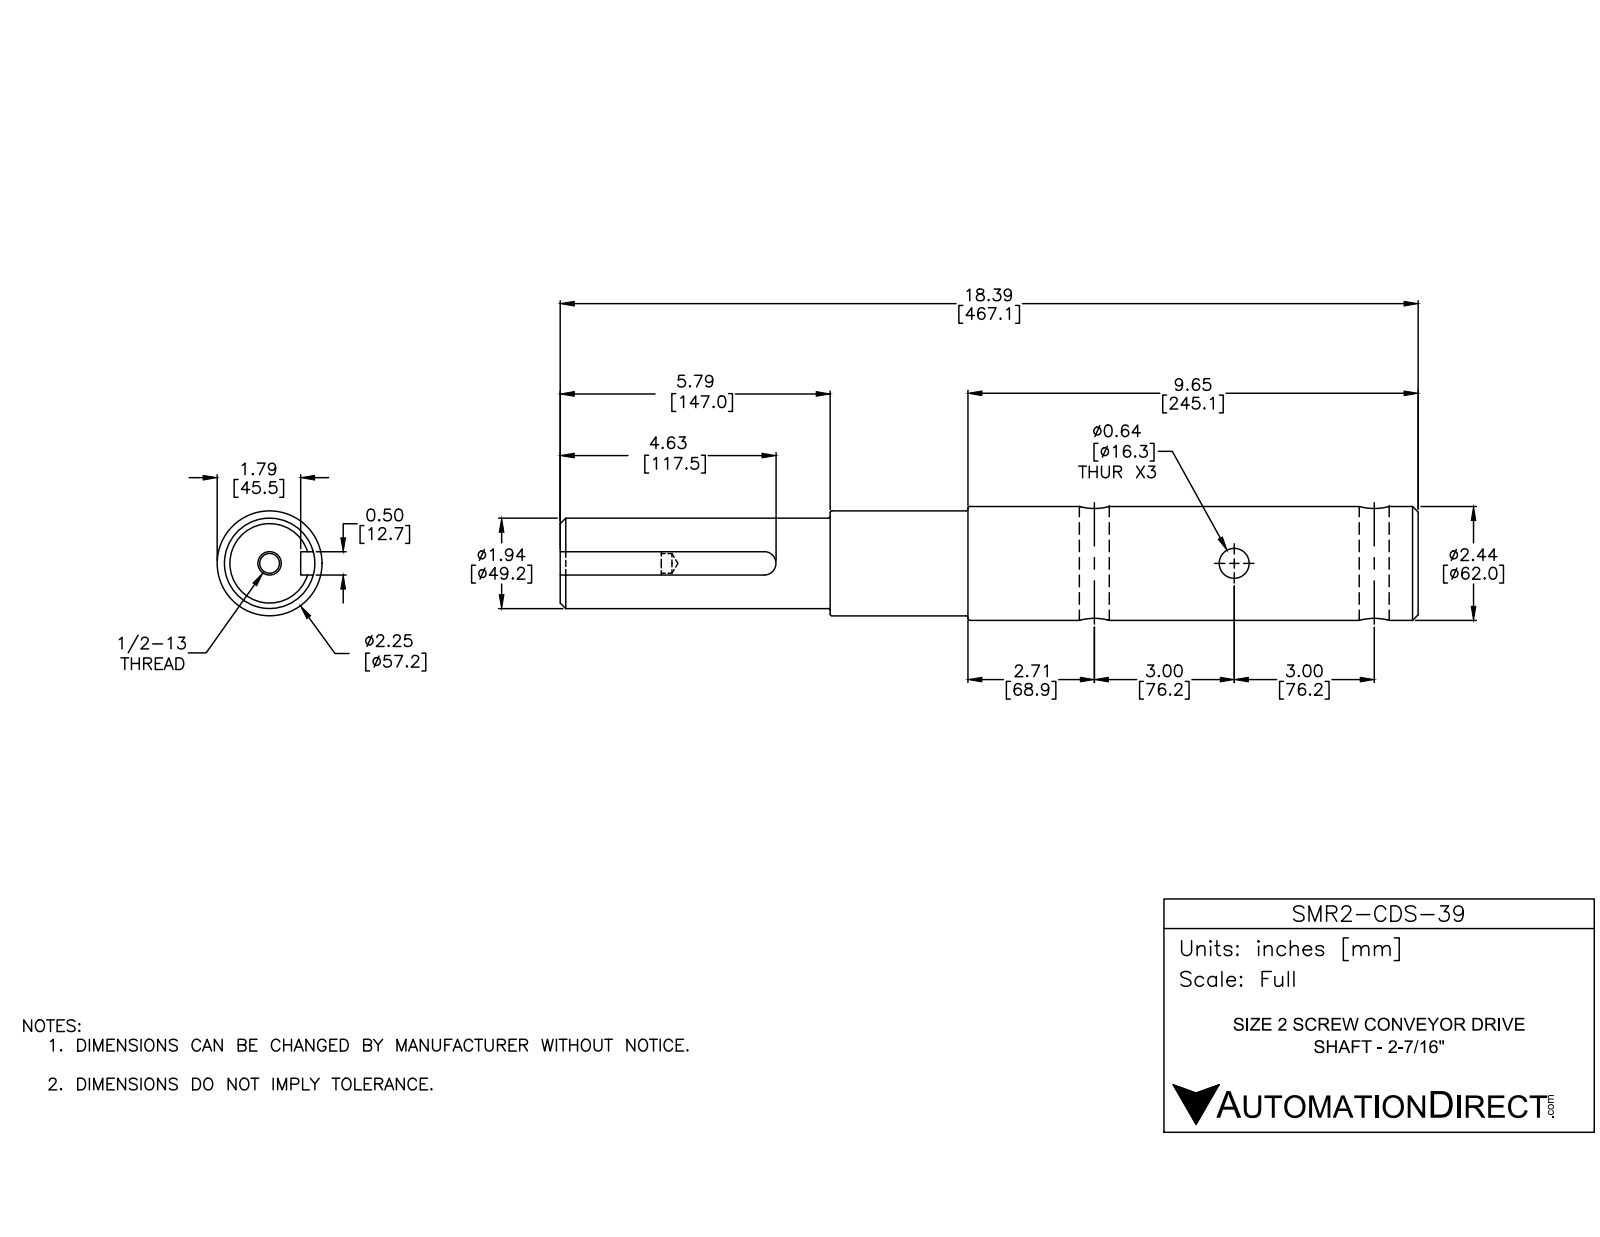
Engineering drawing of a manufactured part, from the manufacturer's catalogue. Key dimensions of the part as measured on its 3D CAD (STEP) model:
Part name (STEP PRODUCT): SMR2-CDS-39
STEP written by: SolidWorks 2016 (AUTOMOTIVE_DESIGN)
Units: inches
Bodies: 1 solid, 40 faces (8 planar, 18 cylindrical, 14 other)
Overall size (bounding box): 18.391 × 2.44 × 2.44
Volume: 70.36 in³ · Surface area: 156.7 in²
Round holes (diameter × count): ⌀0.642 ×3, ⌀0.422 ×1, ⌀0.5 ×1
Round bosses / shafts (diameter × count): ⌀2.44 ×1, ⌀2.25 ×1, ⌀1.937 ×1
Partial cylindrical surfaces — rounded edges, fillets, slot ends (radius × count): R0.25 ×1
Main face-to-face distances: 18.391, 0.5, 5.787, 12.604, 8.74, 2.953, 9.651, 2.165, 3.622, 6.575
Hole centre spacings: 6
